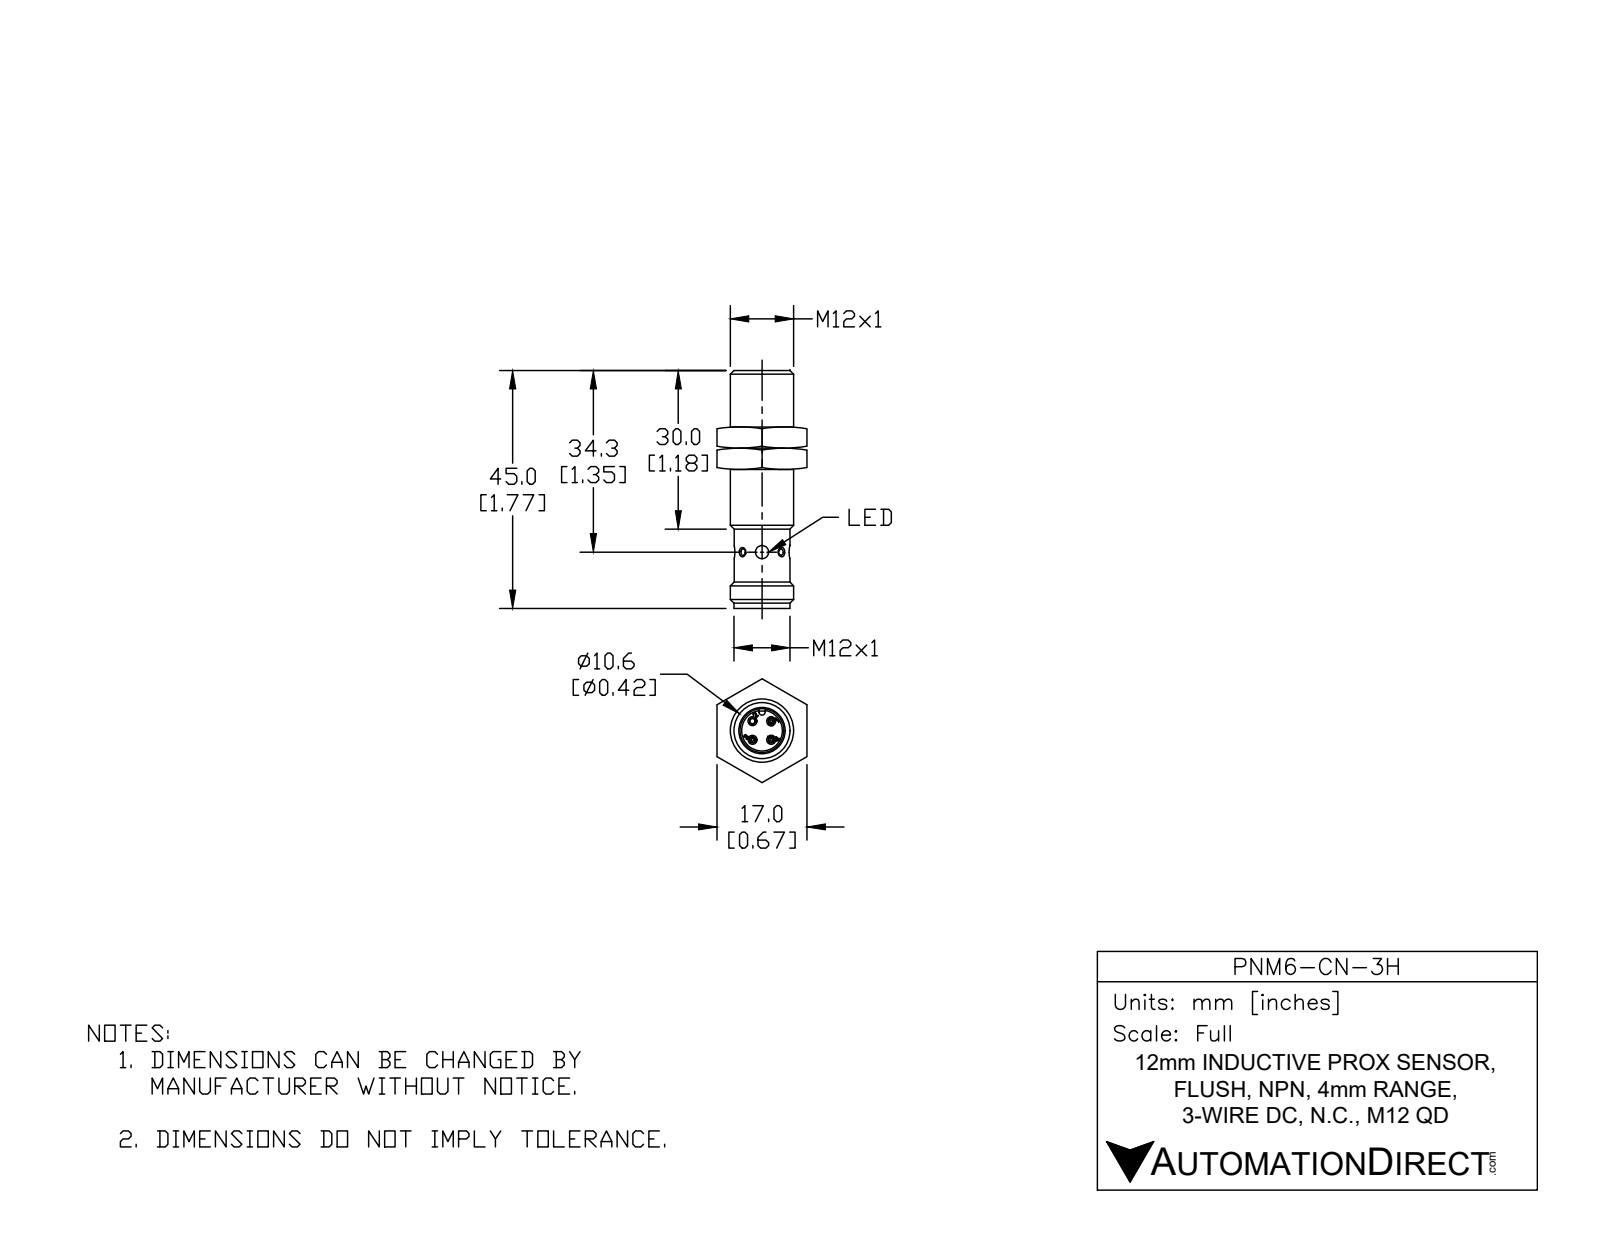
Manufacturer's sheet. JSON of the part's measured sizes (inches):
{"part_name": "PNM6-CN-3H", "step_written_by": "SolidWorks 2017 (AUTOMOTIVE_DESIGN)", "units": "inches", "bodies": {"solids": 1, "faces": 491, "planar": 117, "cylindrical": 138, "other": 236}, "overall_size": [1.772, 0.472, 0.472], "volume_in3": 0.247, "surface_area_in2": 8.016, "round_holes": [[0.043, 3], [0.04, 2], [0.098, 2], [0.038, 1], [0.04, 1], [0.327, 1], [0.394, 1], [0.401, 1]], "round_bosses_or_shafts": [[0.039, 6], [0.472, 1], [0.417, 1], [0.415, 1], [0.4, 1], [0.392, 1], [0.39, 1], [0.38, 1]], "partial_cylinders_radius": [[0.004, 36], [0.079, 6], [0.024, 1], [0.031, 1], [0.161, 1]], "face_to_face_distances": [0.118, 1.299, 1.181, 0.018, 0.1, 1.281, 1.303, 1.421, 1.404, 0.122], "hole_center_spacings": [0.098, 0.139, 0.197]}
